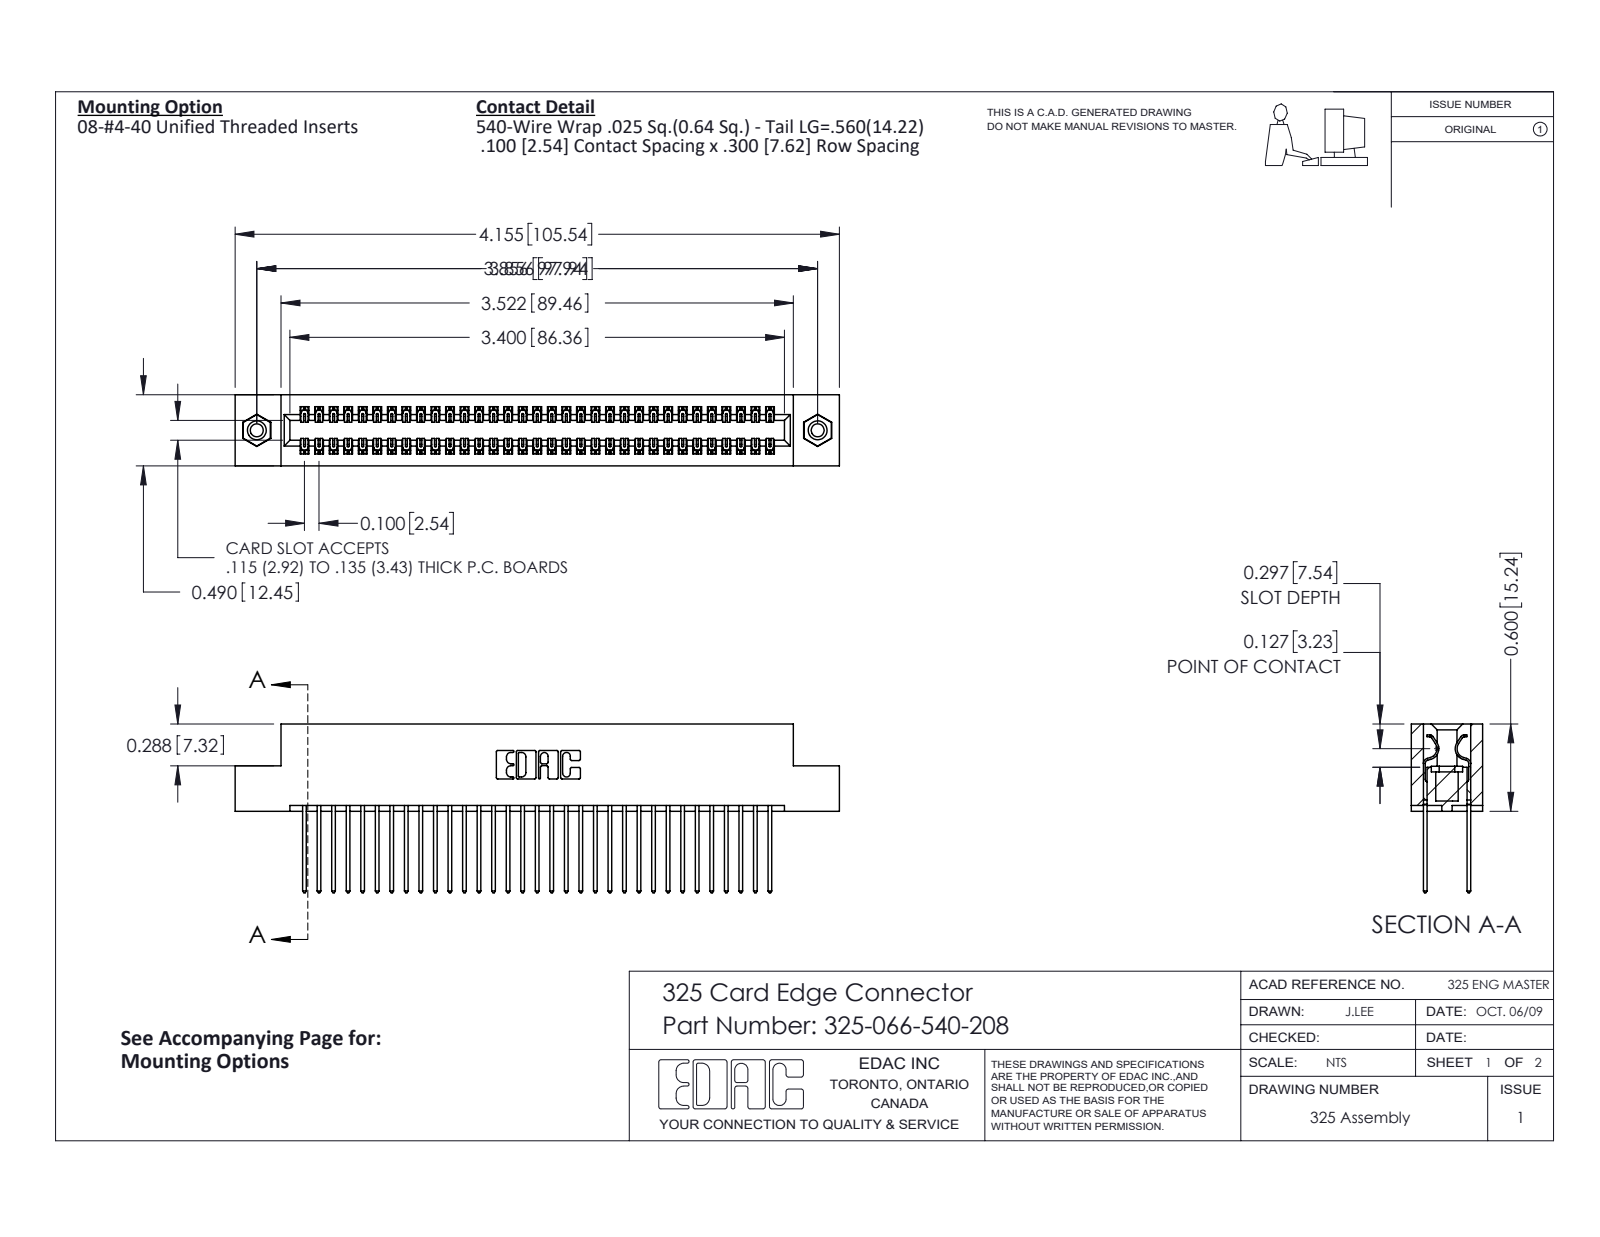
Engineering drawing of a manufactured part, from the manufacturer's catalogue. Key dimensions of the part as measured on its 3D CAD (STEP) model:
Part name (STEP PRODUCT): 325 Part_TI; 325-066-540-208; 325-292-001_325-293-140; 345-250-001_345-250-003-102
STEP written by: SolidWorks 2016 (CONFIG_CONTROL_DESIGN)
Units: inches
Bodies: 69 solids, 3606 faces (2478 planar, 1112 cylindrical, 16 other)
Overall size (bounding box): 4.155 × 1.16 × 0.49
Volume: 0.841 in³ · Surface area: 27.4 in²
Round holes (diameter × count): ⌀0.089 ×2, ⌀0.125 ×2, ⌀0.16 ×2
Round bosses / shafts (diameter × count): ⌀0.155 ×2
Partial cylindrical surfaces — rounded edges, fillets, slot ends (radius × count): R0.006 ×99, R0.01 ×66, R0.01 ×22, R0.007 ×6, R0.031 ×6, R0.026 ×3, R0.014 ×2, R0.022 ×2
Main face-to-face distances: 0.083, 0.407, 0.3, 0.107, 0.383, 0.025, 0.49, 0.325, 0.275, 0.56
Hole centre spacings: 3.856
